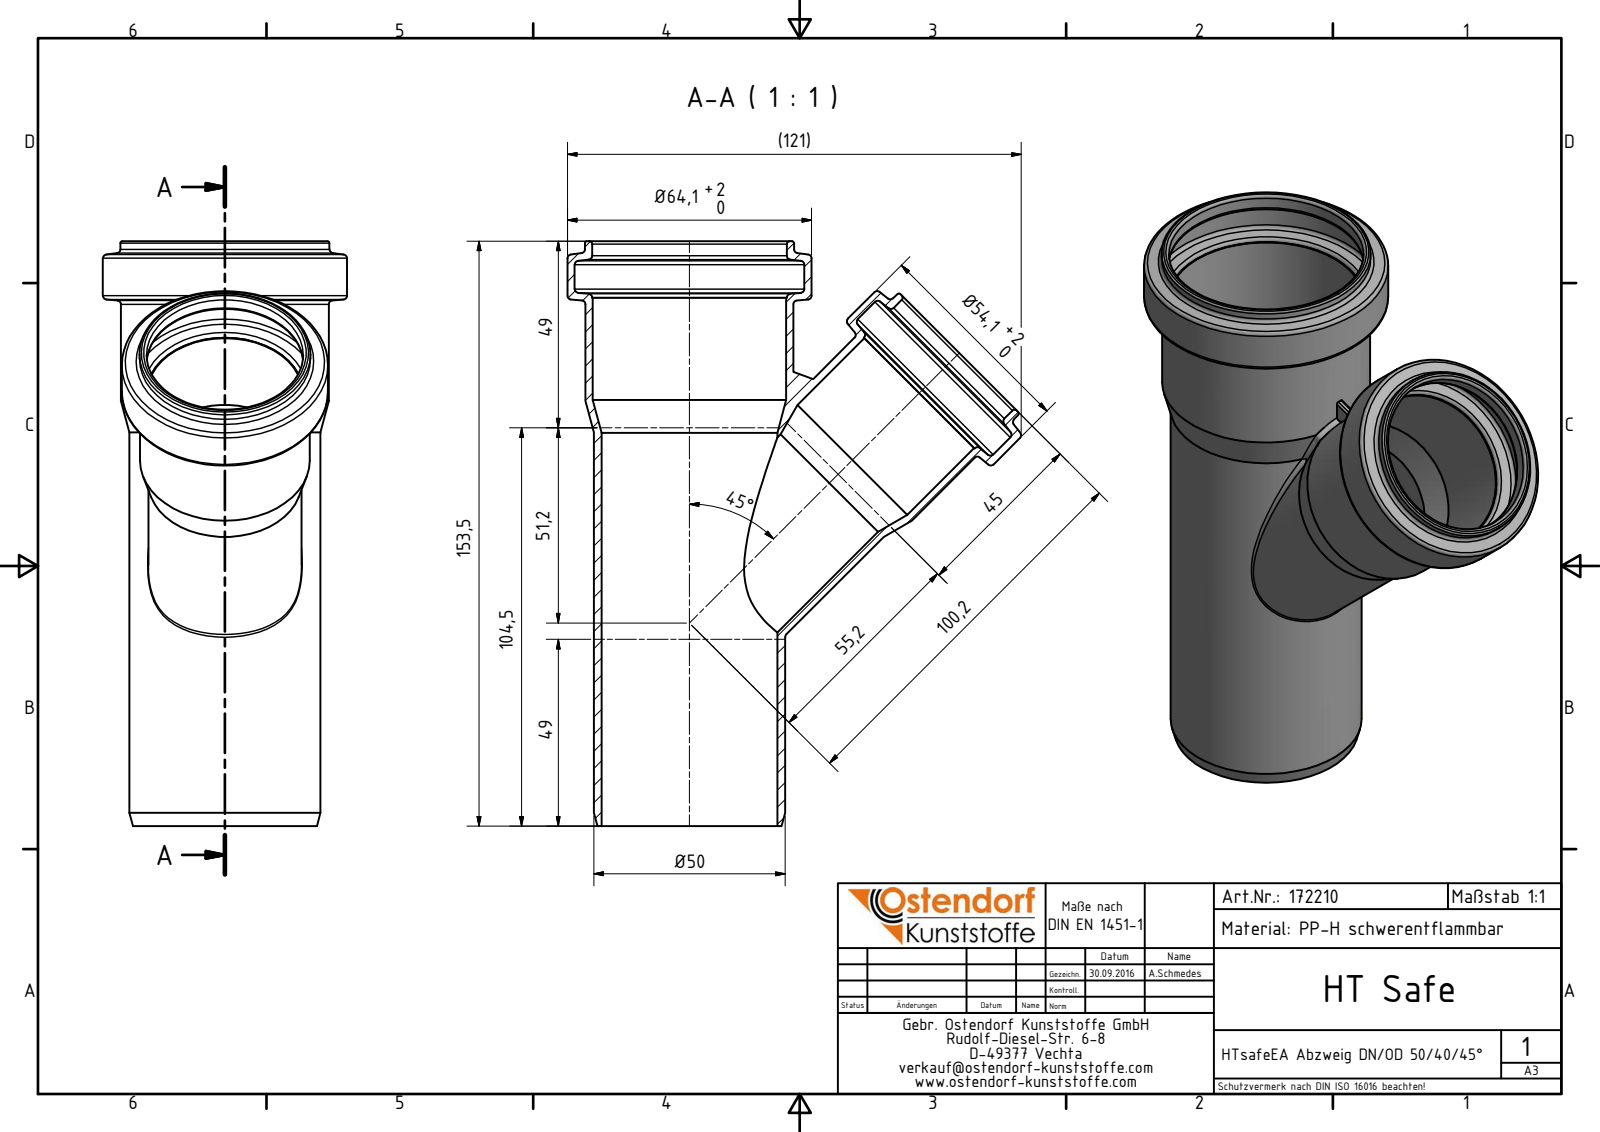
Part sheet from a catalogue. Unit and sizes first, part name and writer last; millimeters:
Units: millimetres
Overall size (bounding box): 153.5 × 119.15 × 64.1
Round holes (diameter × count): ⌀41.1 ×2, ⌀36.2 ×1, ⌀40.8 ×1, ⌀46.2 ×1, ⌀50.3 ×1, ⌀50.8 ×1, ⌀51.1 ×1, ⌀60.3 ×1
Round bosses / shafts (diameter × count): ⌀64.1 ×1, ⌀54.9 ×1, ⌀54.6 ×1, ⌀54.1 ×1, ⌀50.2 ×1, ⌀44.9 ×1, ⌀44.6 ×1, ⌀40.2 ×1
Partial cylindrical surfaces — rounded edges, fillets, slot ends (radius × count): R0.5 ×2
Main face-to-face distances: 153.5, 138.6, 14.9, 14.89, 2
Volume: 67 632 mm³ · Surface area: 69 237 mm²
Bodies: 1 solid, 68 faces (8 planar, 20 cylindrical, 40 other)
Part name (STEP PRODUCT): 172210 HTsafeEA DN_OD 50_40_45°
STEP written by: Autodesk Inventor 2016 (AUTOMOTIVE_DESIGN)
